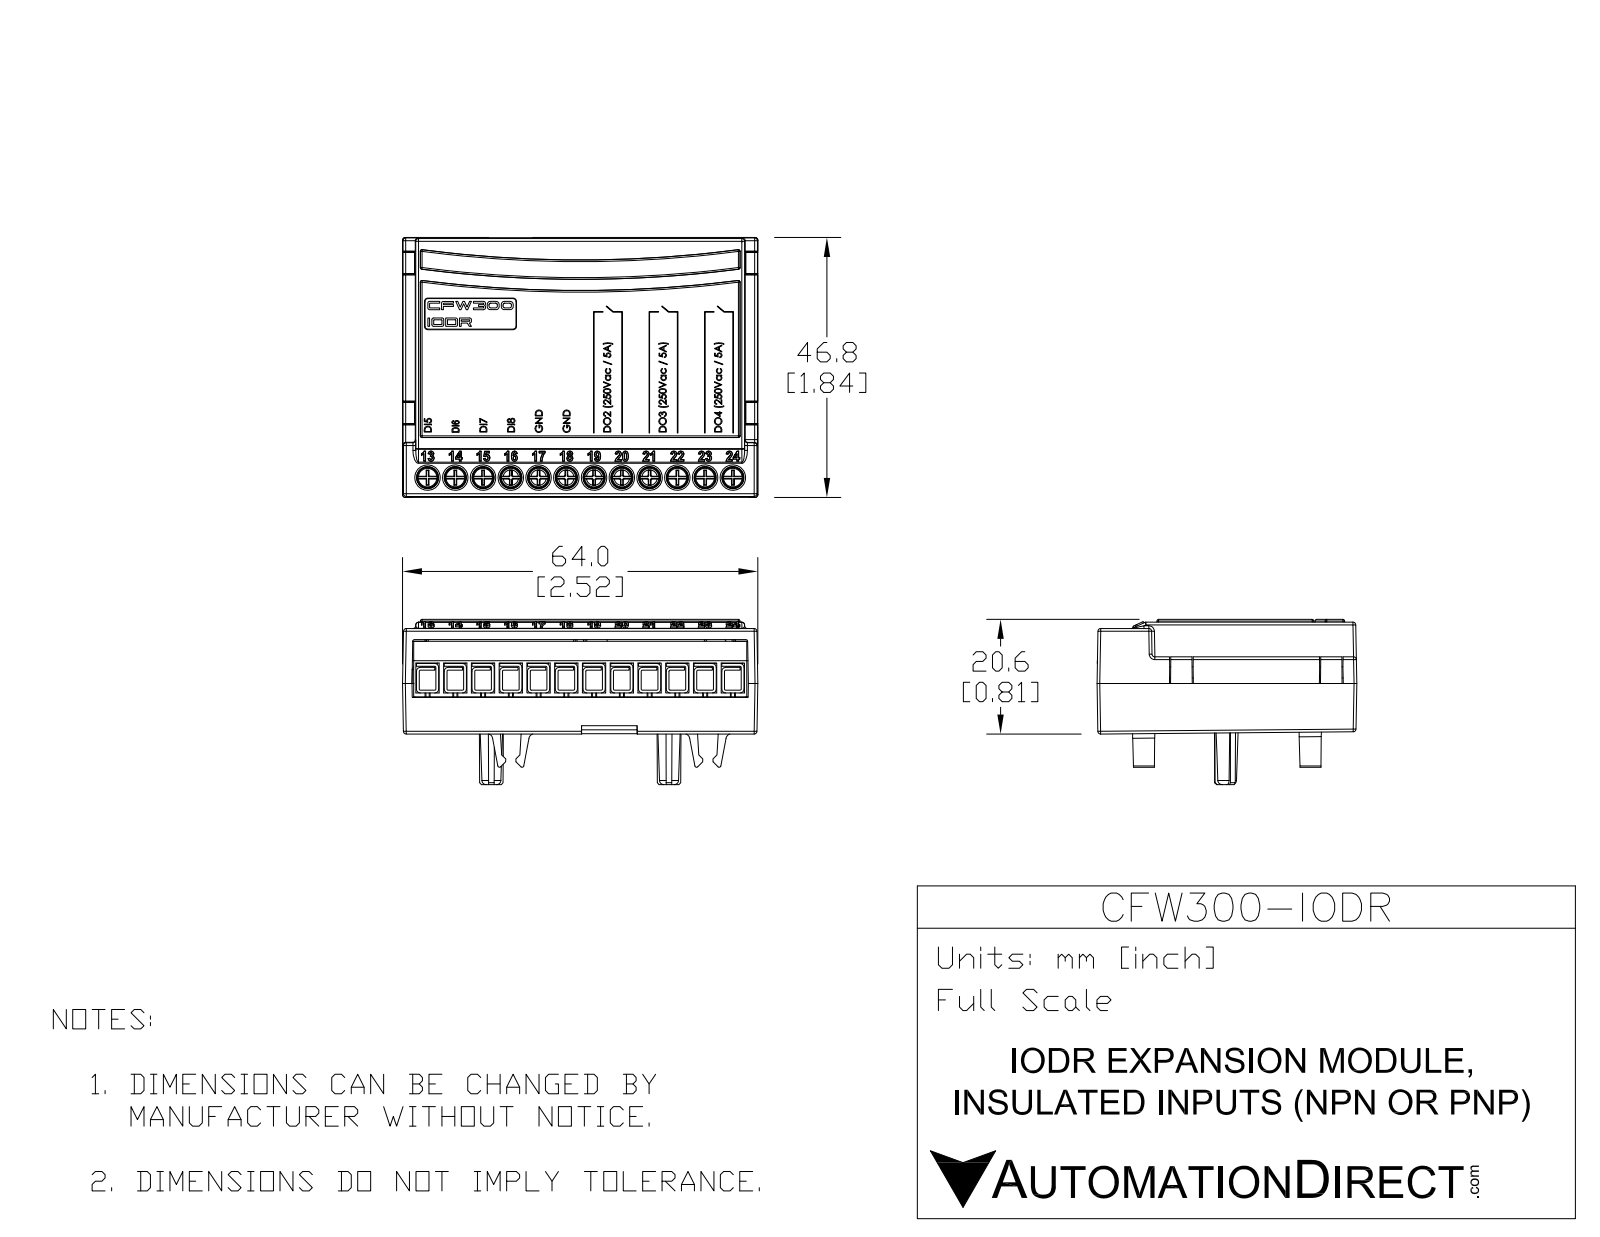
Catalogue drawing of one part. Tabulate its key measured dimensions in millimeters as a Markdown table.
| quantity | value |
| --- | --- |
| part name | CFW300-IODR |
| STEP written by | SolidWorks 2017 (AUTOMOTIVE_DESIGN) |
| units | millimeters |
| bodies | 13 solids, 1761 faces (1006 planar, 195 cylindrical, 560 other) |
| overall size | 64 × 47.1 × 20.7 |
| volume | 58 060 mm³ |
| surface area | 15 410 mm² |
| round holes (diameter × count) | 4.6 × 12 |
| round bosses / shafts (diameter × count) | 3.9 × 12 |
| partial cylindrical surfaces (radius × count) | 0.2 × 48, 0.7 × 48, 1 × 16, 0.5 × 4, 0.6 × 4, 0.3 × 3 |
| main face-to-face distances | 20.6, 0.5, 47, 64, 4.8, 0.7, 6.8, 2.3, 61.7, 1.2 |
| hole center spacings | 5, 10, 15, 20, 25, 30, 35, 40 |
